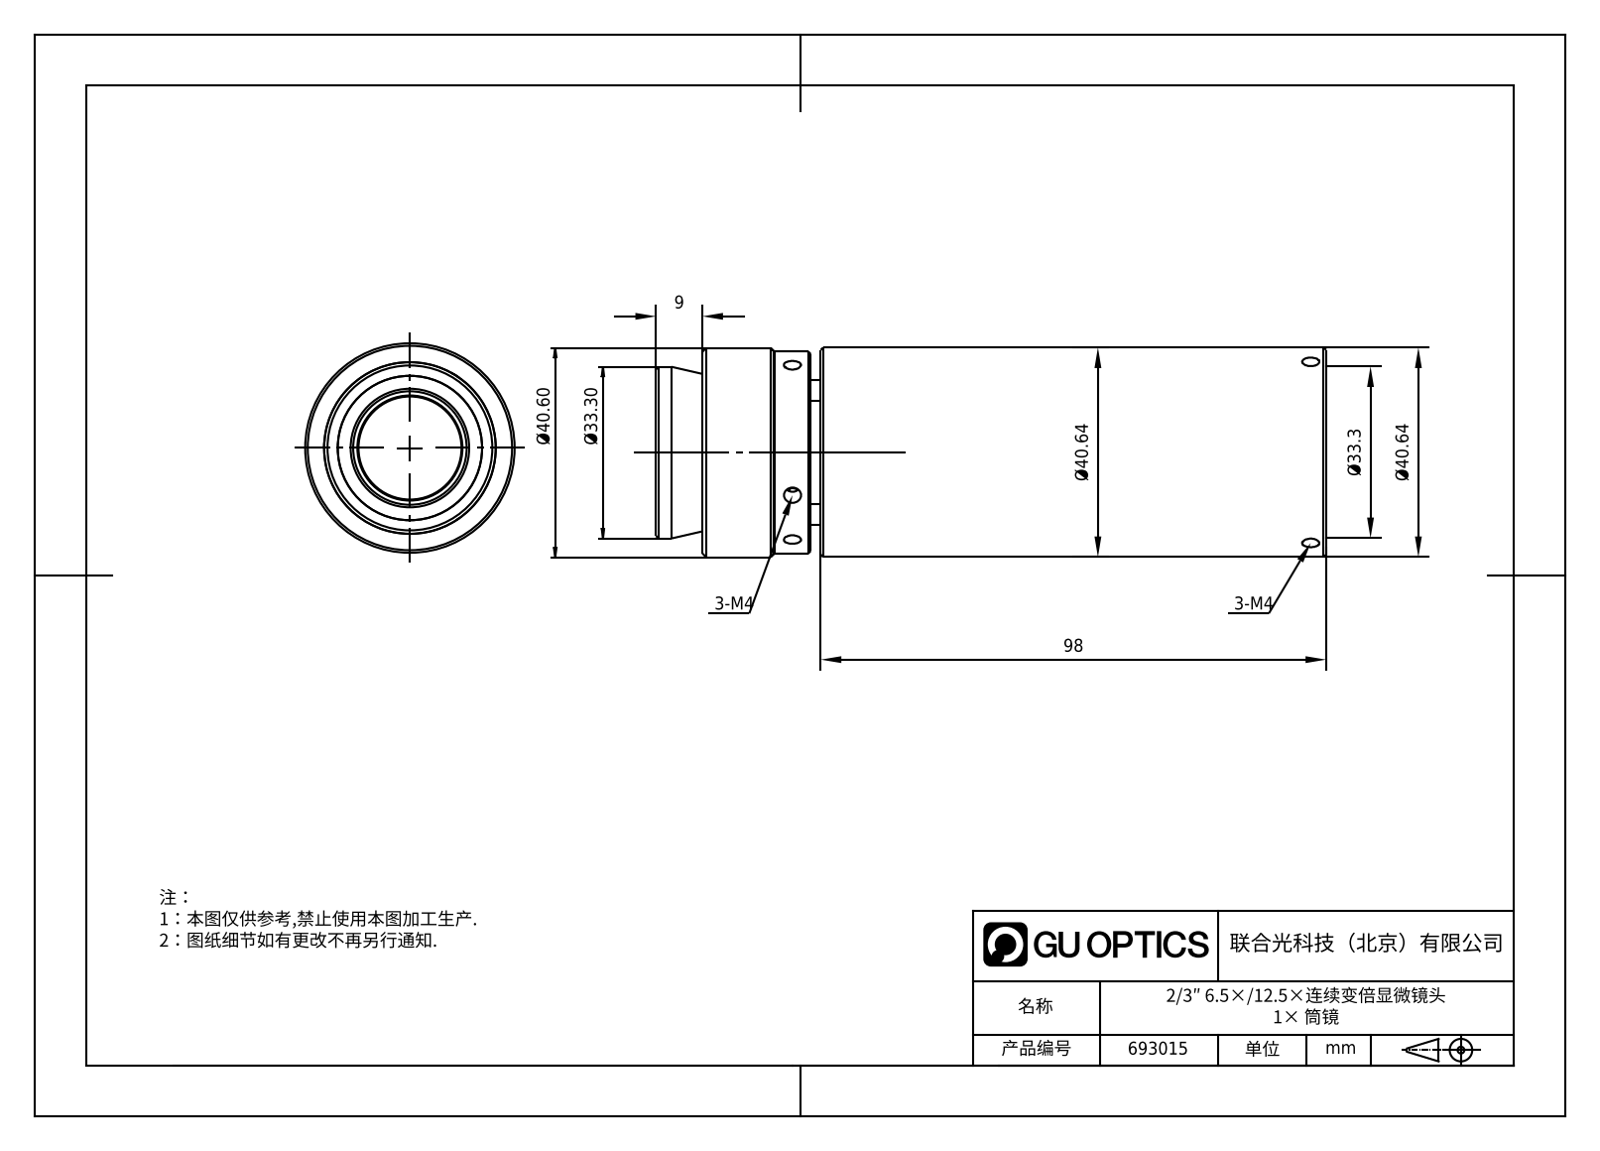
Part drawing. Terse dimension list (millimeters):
name: 693015
written by: SolidWorks 2020 (CONFIG_CONTROL_DESIGN)
unit: mm
bodies: 0 solids, 35 faces (11 planar, 17 cylindrical, 7 other)
size: 130 × 40.64 × 40.64
holes: 6× ⌀3.3, 1× ⌀32
bosses: 1× ⌀40.64, 1× ⌀40.6, 1× ⌀39.14, 1× ⌀39.1, 1× ⌀33.3, 1× ⌀23, 1× ⌀20
face distances: 8.5, 8.51, 8.49, 0.5, 9, 31.5, 31.49, 23, 22.99, 29.5
hole spacings: 100.5
